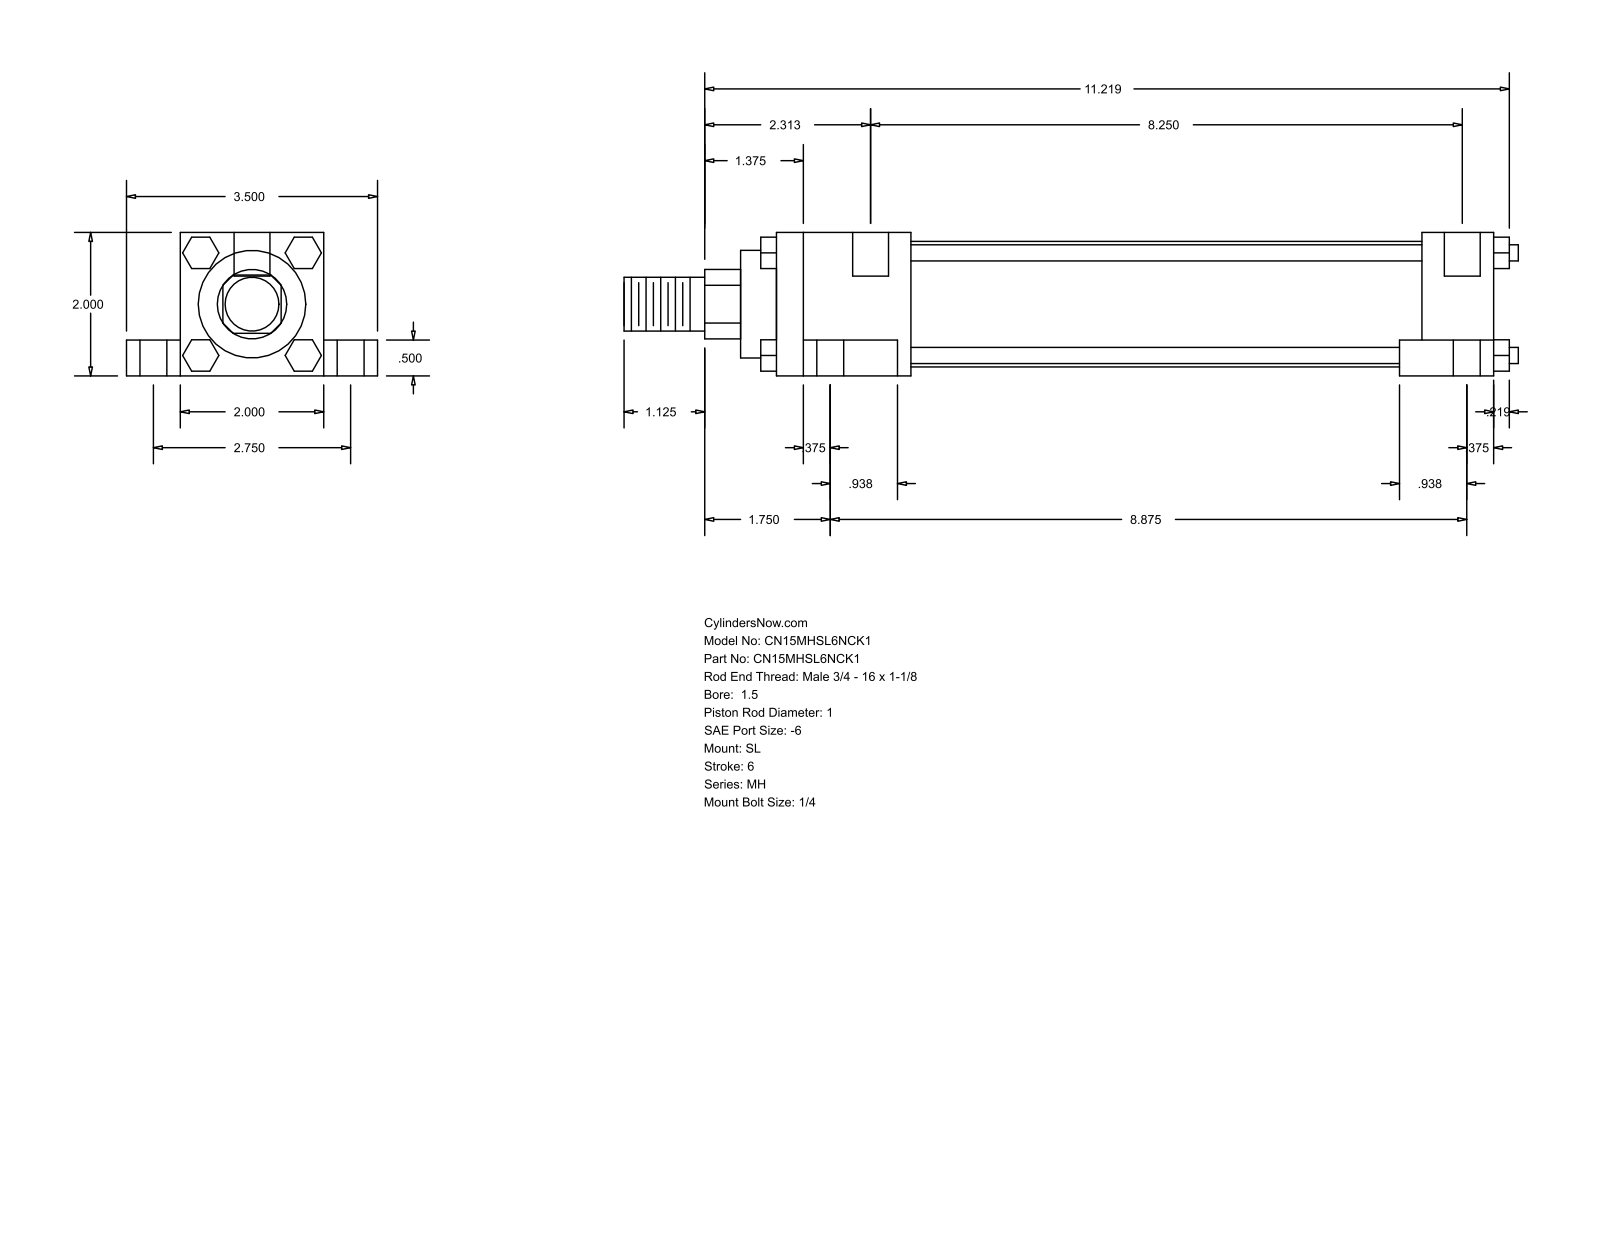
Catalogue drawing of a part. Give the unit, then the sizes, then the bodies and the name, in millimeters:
Units: millimetres
Overall size (bounding box): 316.71 × 88.9 × 50.8
Round holes (diameter × count): ⌀5.56 ×4, ⌀9.53 ×4, ⌀15.88 ×4, ⌀12.7 ×2
Round bosses / shafts (diameter × count): ⌀5.71 ×4, ⌀44.45 ×1, ⌀38.1 ×1, ⌀25.4 ×1, ⌀19.05 ×1
Partial cylindrical surfaces — rounded edges, fillets, slot ends (radius × count): R12.29 ×1
Main face-to-face distances: 50.8, 12.7, 38.1, 19.05, 69.85, 254, 25.4, 9.52, 33.34, 211.14
Hole centre spacings: 34.96, 36.64, 37.73, 69.84, 212.73, 214.01, 217.15, 225.43
Bodies: 0 solids, 148 faces (112 planar, 36 cylindrical, 0 other)
Part name (STEP PRODUCT): MH_SL__0150_1
STEP written by: GSSL Pune (CONFIG_CONTROL_DESIGN)
